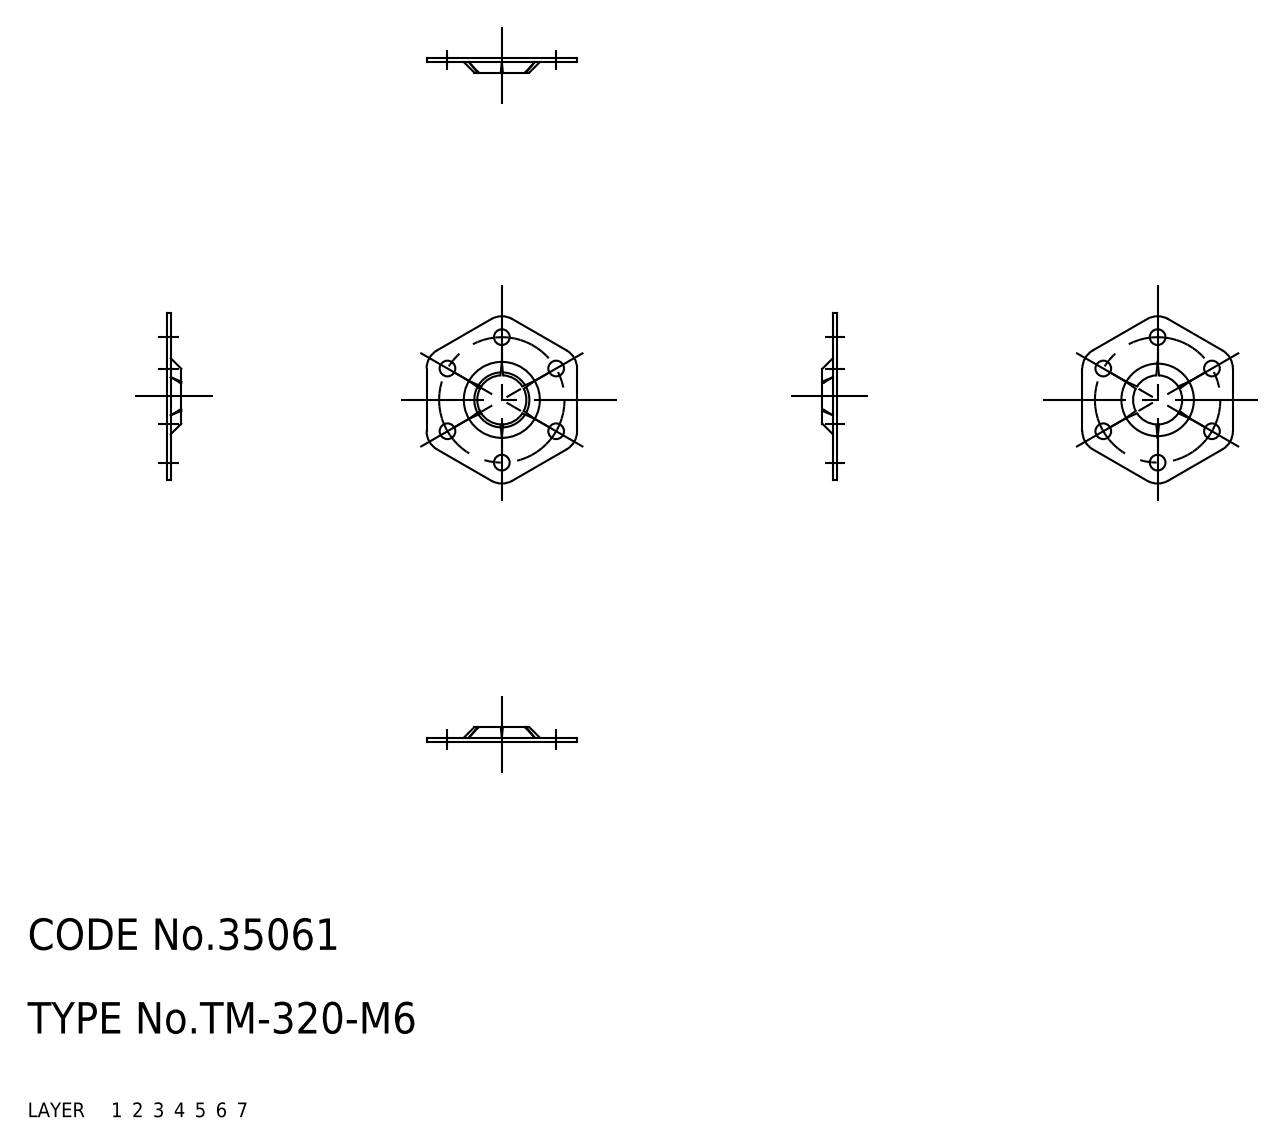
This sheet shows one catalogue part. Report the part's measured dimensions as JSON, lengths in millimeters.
{"part_name": "67112178", "step_written_by": "CADfix (AUTOMOTIVE_DESIGN)", "units": "millimeters", "bodies": {"solids": 1, "faces": 62, "planar": 0, "cylindrical": 0, "other": 62}, "overall_size": [16, 14.39, 1.4], "volume_mm3": 62, "surface_area_mm2": 354}
